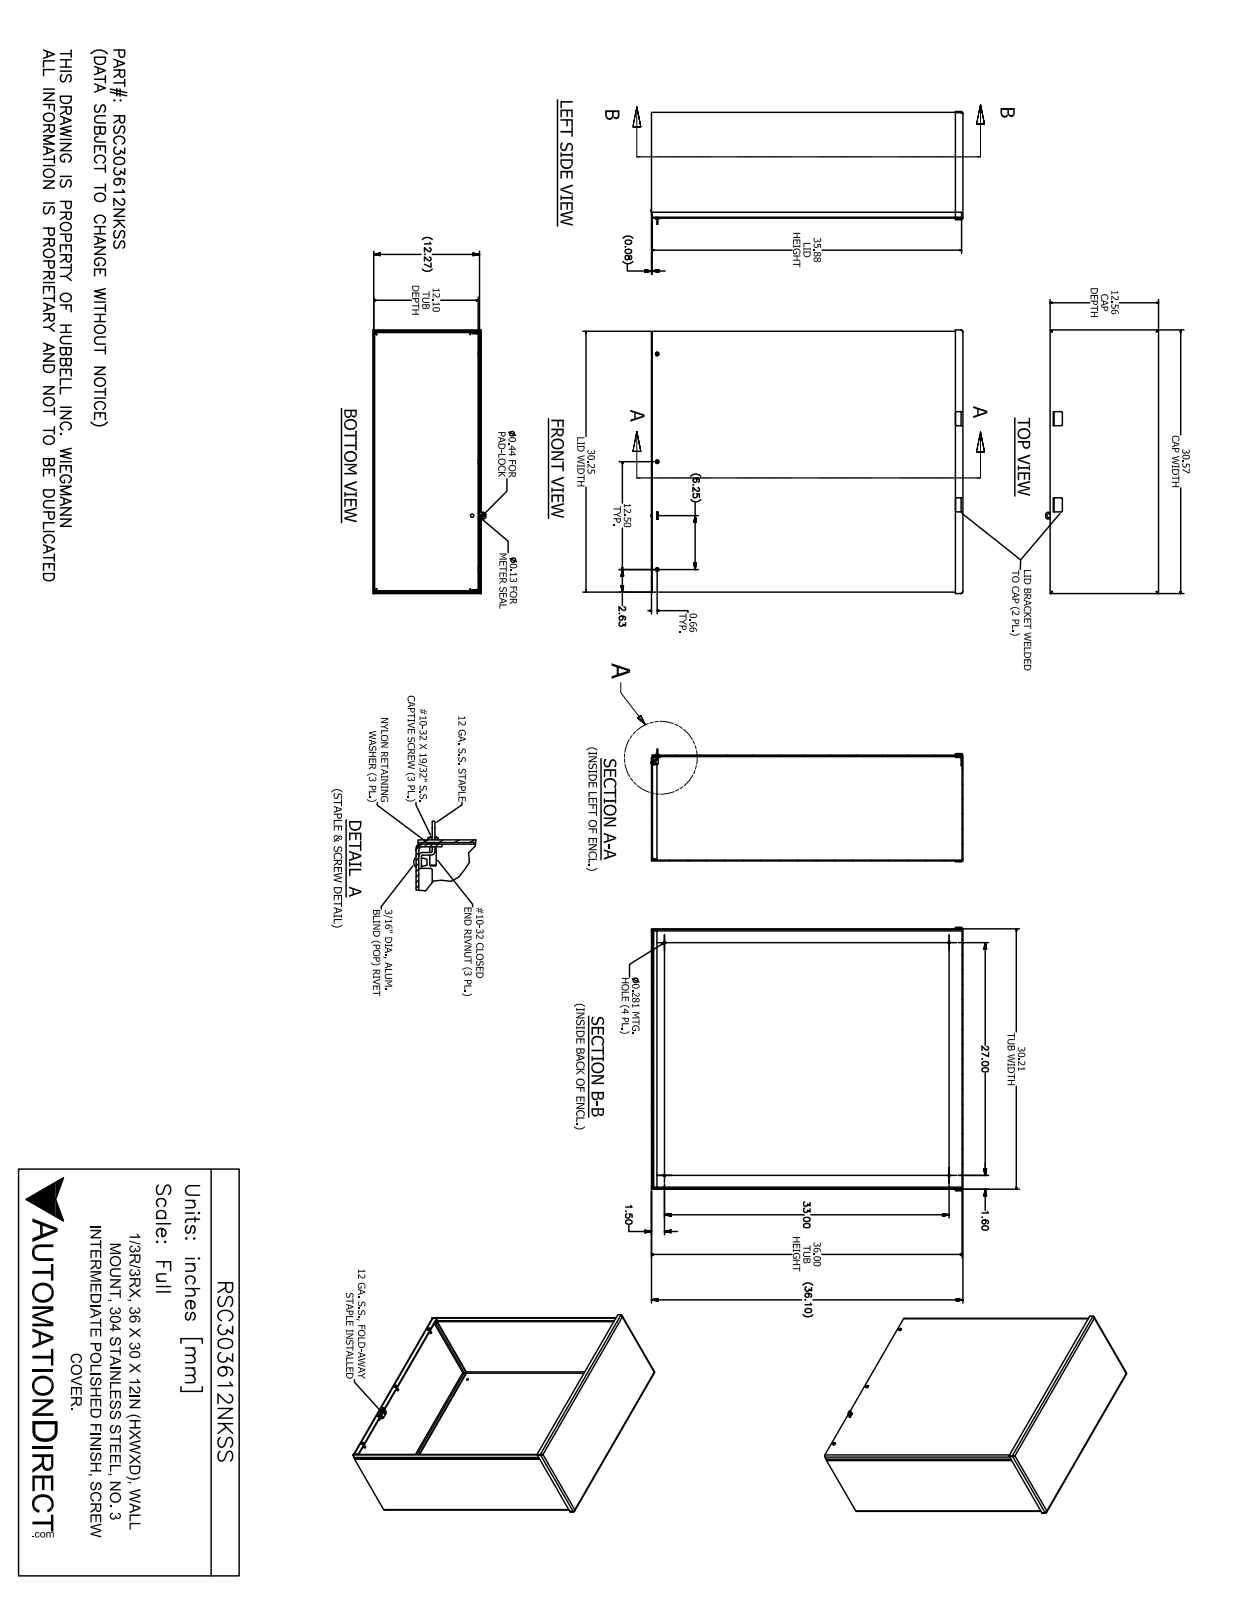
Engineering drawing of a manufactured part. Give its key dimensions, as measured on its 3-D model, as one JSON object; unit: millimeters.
{"part_name": "RSC303612NKSS", "step_written_by": "SolidWorks 2017 (AUTOMOTIVE_DESIGN)", "units": "millimeters", "bodies": {"solids": 17, "faces": 440, "planar": 241, "cylindrical": 117, "other": 82}, "overall_size": [919.3, 776.5, 332.6], "volume_mm3": 6689000, "surface_area_mm2": 5103000, "round_holes": [[6.4, 6], [7.1, 4], [4, 3], [5, 3], [6.5, 3], [7.1, 3], [3.2, 1], [5, 1], [5.1, 1], [11.1, 1]], "round_bosses_or_shafts": [[11.5, 3], [10.3, 3], [6.3, 3], [4.2, 3], [4.7, 1]], "partial_cylinders_radius": [[3.6, 14], [6.2, 14], [3.2, 9], [0.8, 6], [6.4, 4], [2.3, 3], [1.2, 2], [1.6, 2]], "face_to_face_distances": [2.6, 308.9, 311.6, 306.3, 764.6, 914.4, 767.3, 762, 917, 911.8], "hole_center_spacings": [317.5, 937.3, 881.9, 33.2, 33.8, 343.6, 343.6, 635]}
